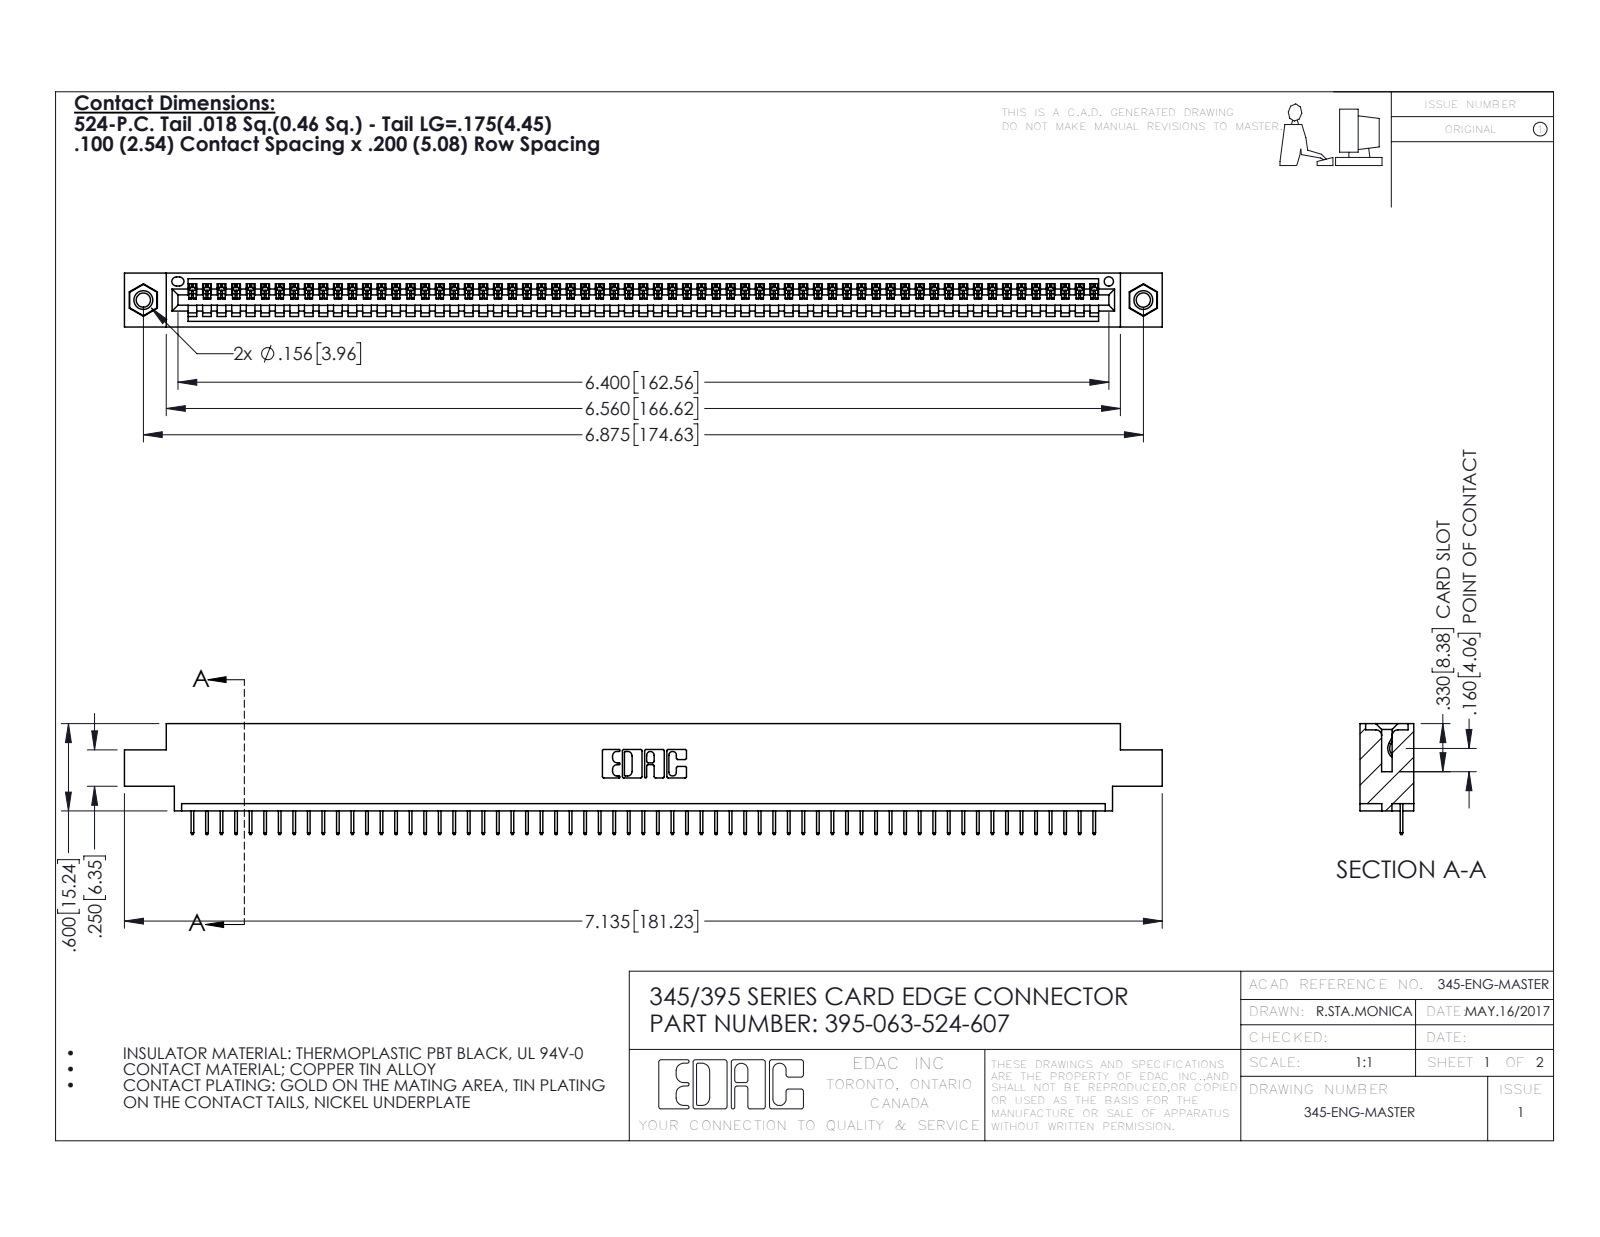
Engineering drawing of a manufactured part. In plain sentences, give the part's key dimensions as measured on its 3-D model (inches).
The part is named "345-250-001_345-250-005-103; 345 Part_0.170 Offset - 0.156 Dia-TI; 395-063-524-607; 345-292-001_345-293-124". Its 3-D file was written by "SolidWorks 2016 (CONFIG_CONTROL_DESIGN)". It is 66 solids with 4096 faces: 3014 planar, 1066 cylindrical and 16 other. Overall it measures 7.135 by 0.762 by 0.37 inches. Its volume is 1.038 cubic inches and its surface area 34.49 square inches. Round holes: 2 of diameter 0.098, 2 of diameter 0.125, 2 of diameter 0.156, 1 of diameter 0.064. Round bosses or shafts: 2 of diameter 0.155. Partial cylindrical surfaces (rounded edges, fillets, slot ends): 126 of radius 0.006, 22 of radius 0.01, 6 of radius 0.007, 6 of radius 0.031, 3 of radius 0.026, 2 of radius 0.031, 2 of radius 0.04, 1 of radius 0.014. The main face-to-face distances are 0.072, 0.298, 0.37, 0.2, 0.098, 0.272, 0.025, 0.225, 0.072, 0.175. The hole center spacings are 0.27, 6.639, 6.875.
